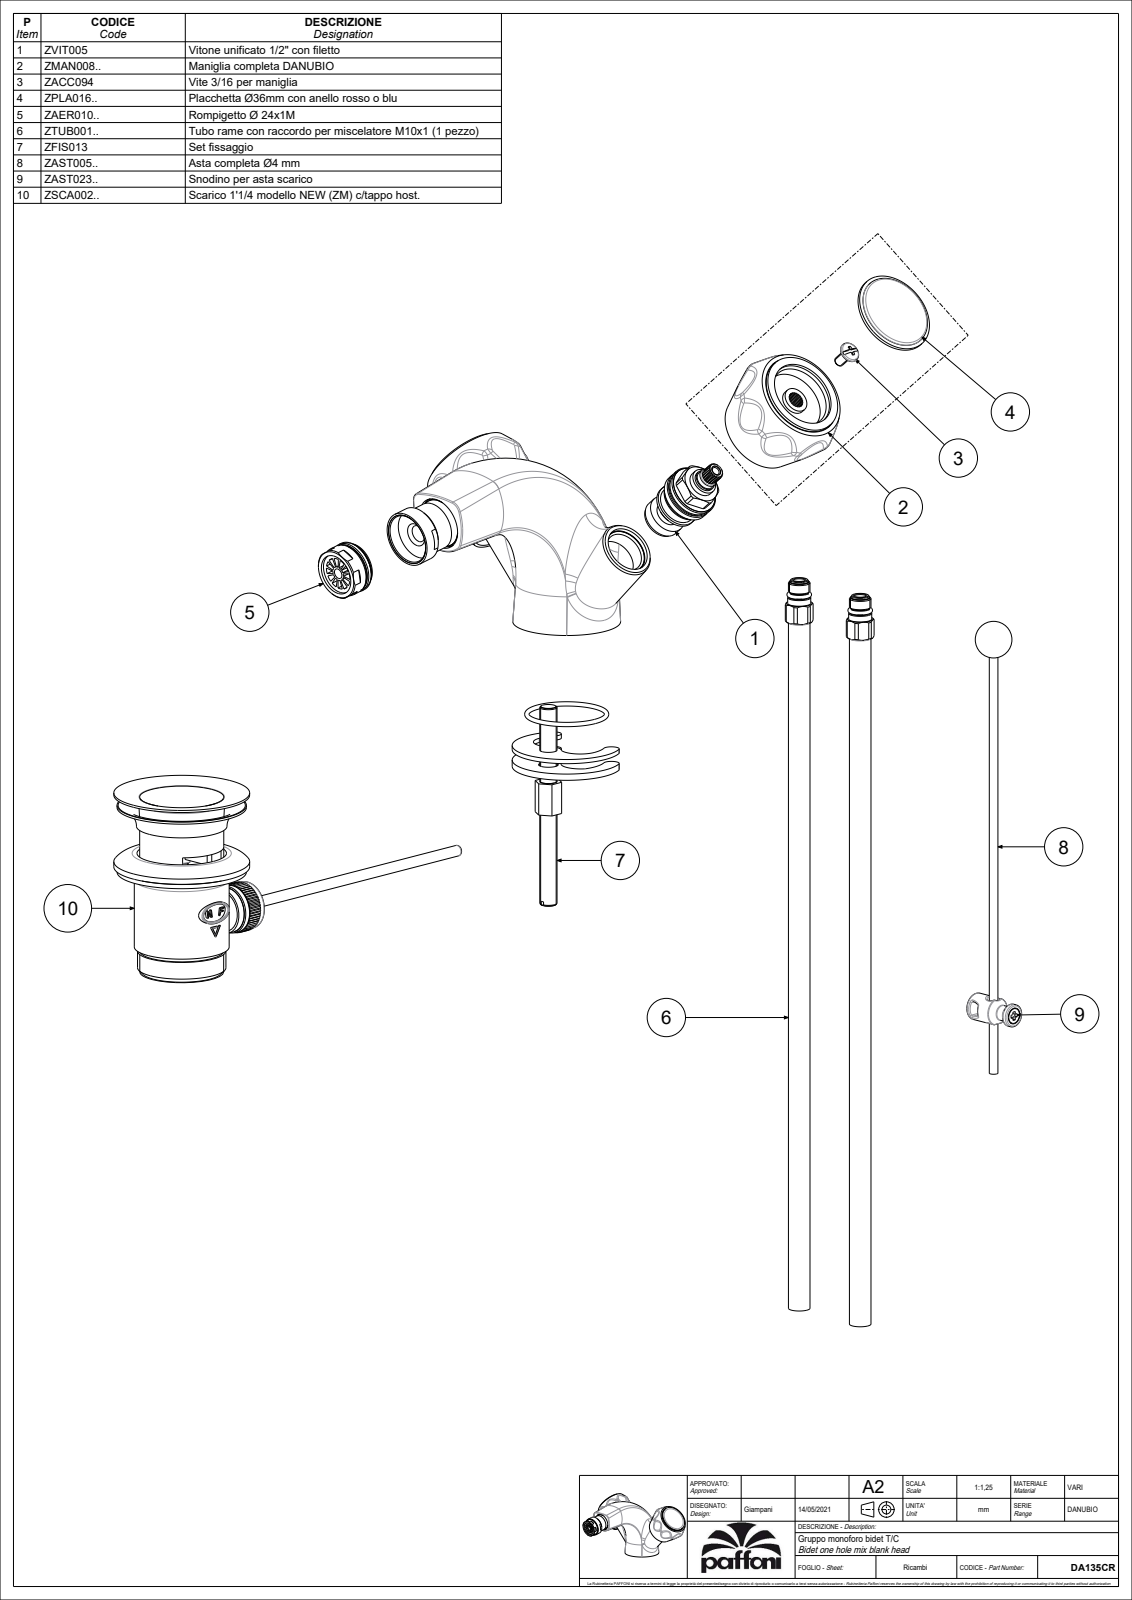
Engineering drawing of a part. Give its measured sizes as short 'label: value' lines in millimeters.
name: DA135CR
written by: CREO PARAMETRIC BY PTC INC, 2020044 (CONFIG_CONTROL_DESIGN)
unit: mm
bodies: 2 solids, 803 faces (221 planar, 214 cylindrical, 368 other)
size: 159.12 × 138.85 × 86.76
volume: 166 013 mm³; area: 84 356 mm²
holes: 3× ⌀8, 3× ⌀19, 2× ⌀5.5, 2× ⌀9, 2× ⌀11, 2× ⌀35.8, 2× ⌀39, 1× ⌀4.8, 1× ⌀5, 1× ⌀15, 1× ⌀15.5, 1× ⌀16
bosses: 3× ⌀24, 3× ⌀22.5, 2× ⌀38.5, 2× ⌀30.5, 2× ⌀18.6, 2× ⌀17.3, 2× ⌀13, 2× ⌀12.5
rounds: 28× R1, 16× R21.31, 2× R3, 2× R5, 2× R8, 2× R10, 2× R13, 2× R13.5
face distances: 6, 40.81, 6.7, 23, 9.5, 11, 34.11, 9.9, 2.8, 43.61
hole spacings: 7.5, 12.5, 10, 15
